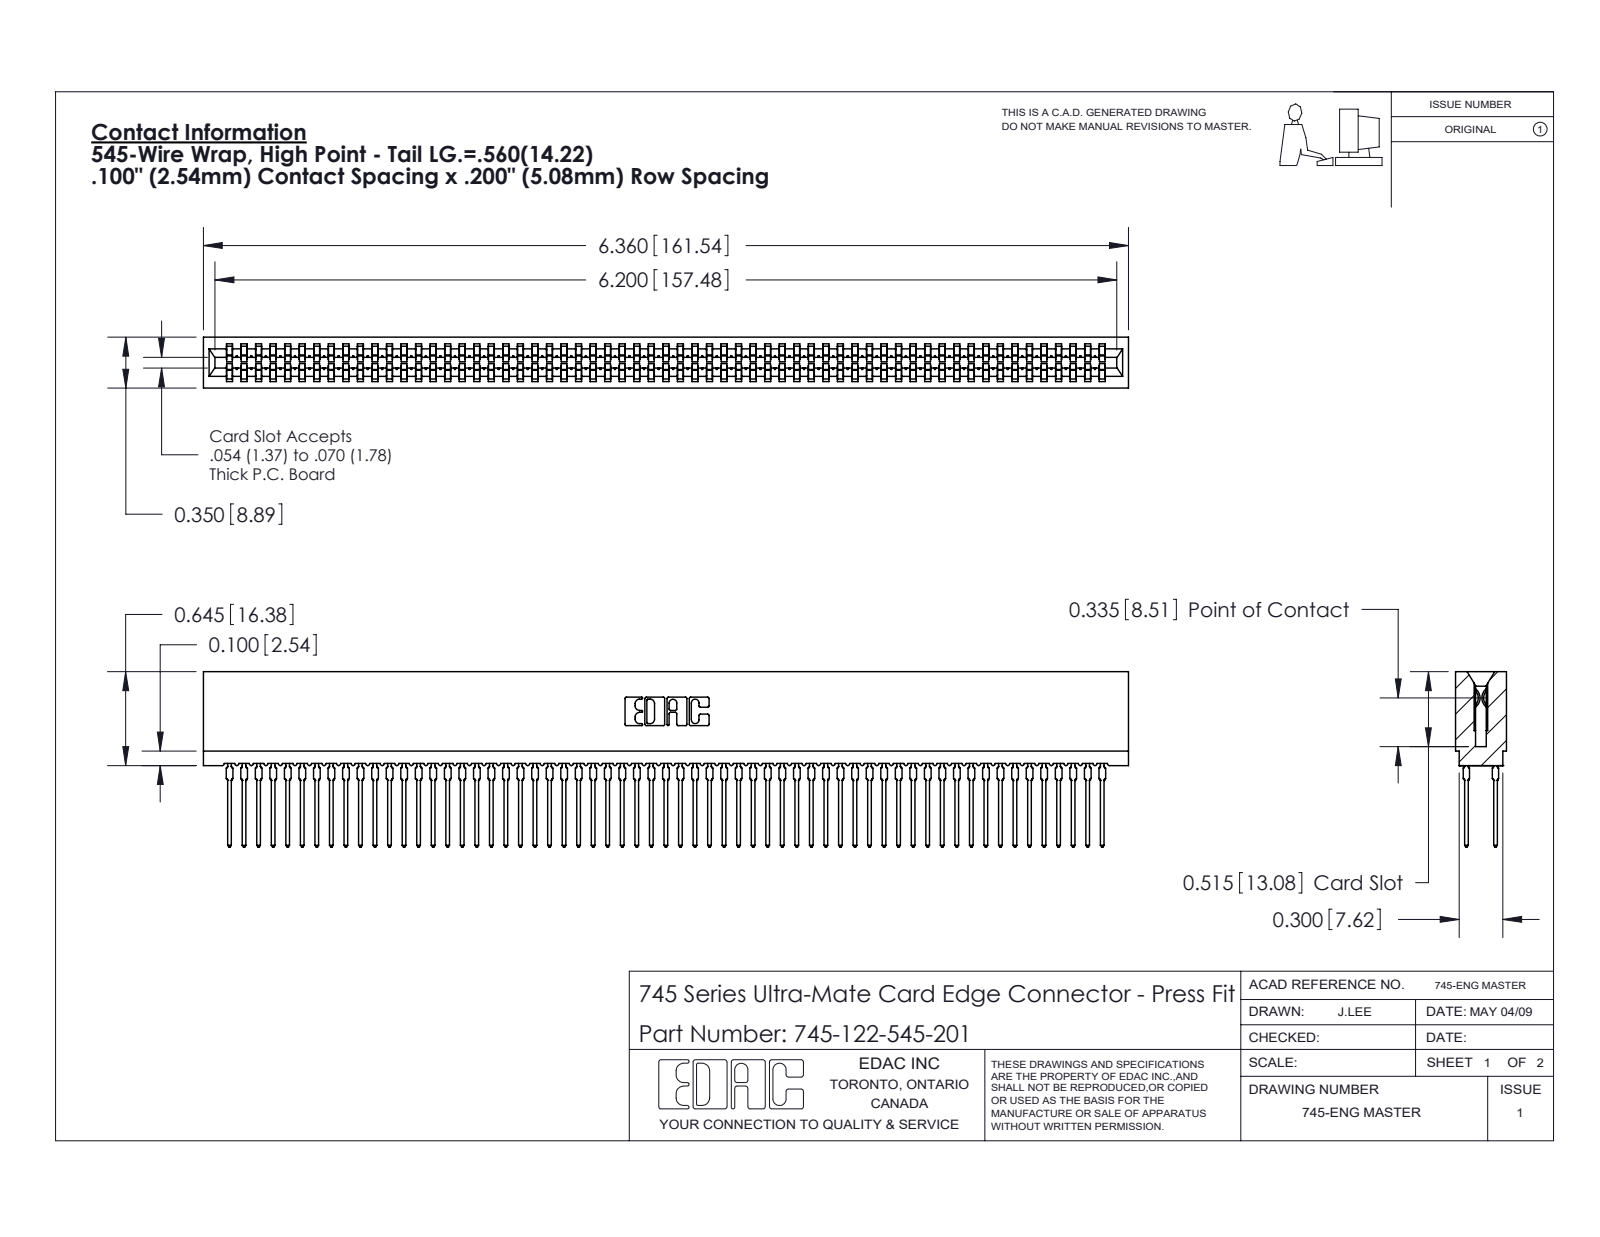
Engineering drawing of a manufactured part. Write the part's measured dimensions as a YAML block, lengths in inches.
part_name: "745-122-545-201; 745-292-001_545; 745 Part_Insulator Option - 01"
step_written_by: "SolidWorks 2020 (CONFIG_CONTROL_DESIGN)"
units: inches
bodies: {solids: 123, faces: 11014, planar: 5667, cylindrical: 2175, other: 3172}
overall_size: [6.36, 1.206, 0.35]
volume: 0.907
surface_area: 50.4
partial_cylinders:
  - {radius: 0.021, count: 244}
  - {radius: 0.015, count: 122}
  - {radius: 0.01, count: 22}
  - {radius: 0.005, count: 8}
  - {radius: 0.011, count: 8}
  - {radius: 0.007, count: 6}
  - {radius: 0.031, count: 6}
  - {radius: 0.026, count: 3}
face_to_face_distances: [0.063, 0.287, 0.35, 0.2, 0.045, 0.305, 0.018, 0.243, 0.138, 0.212]
